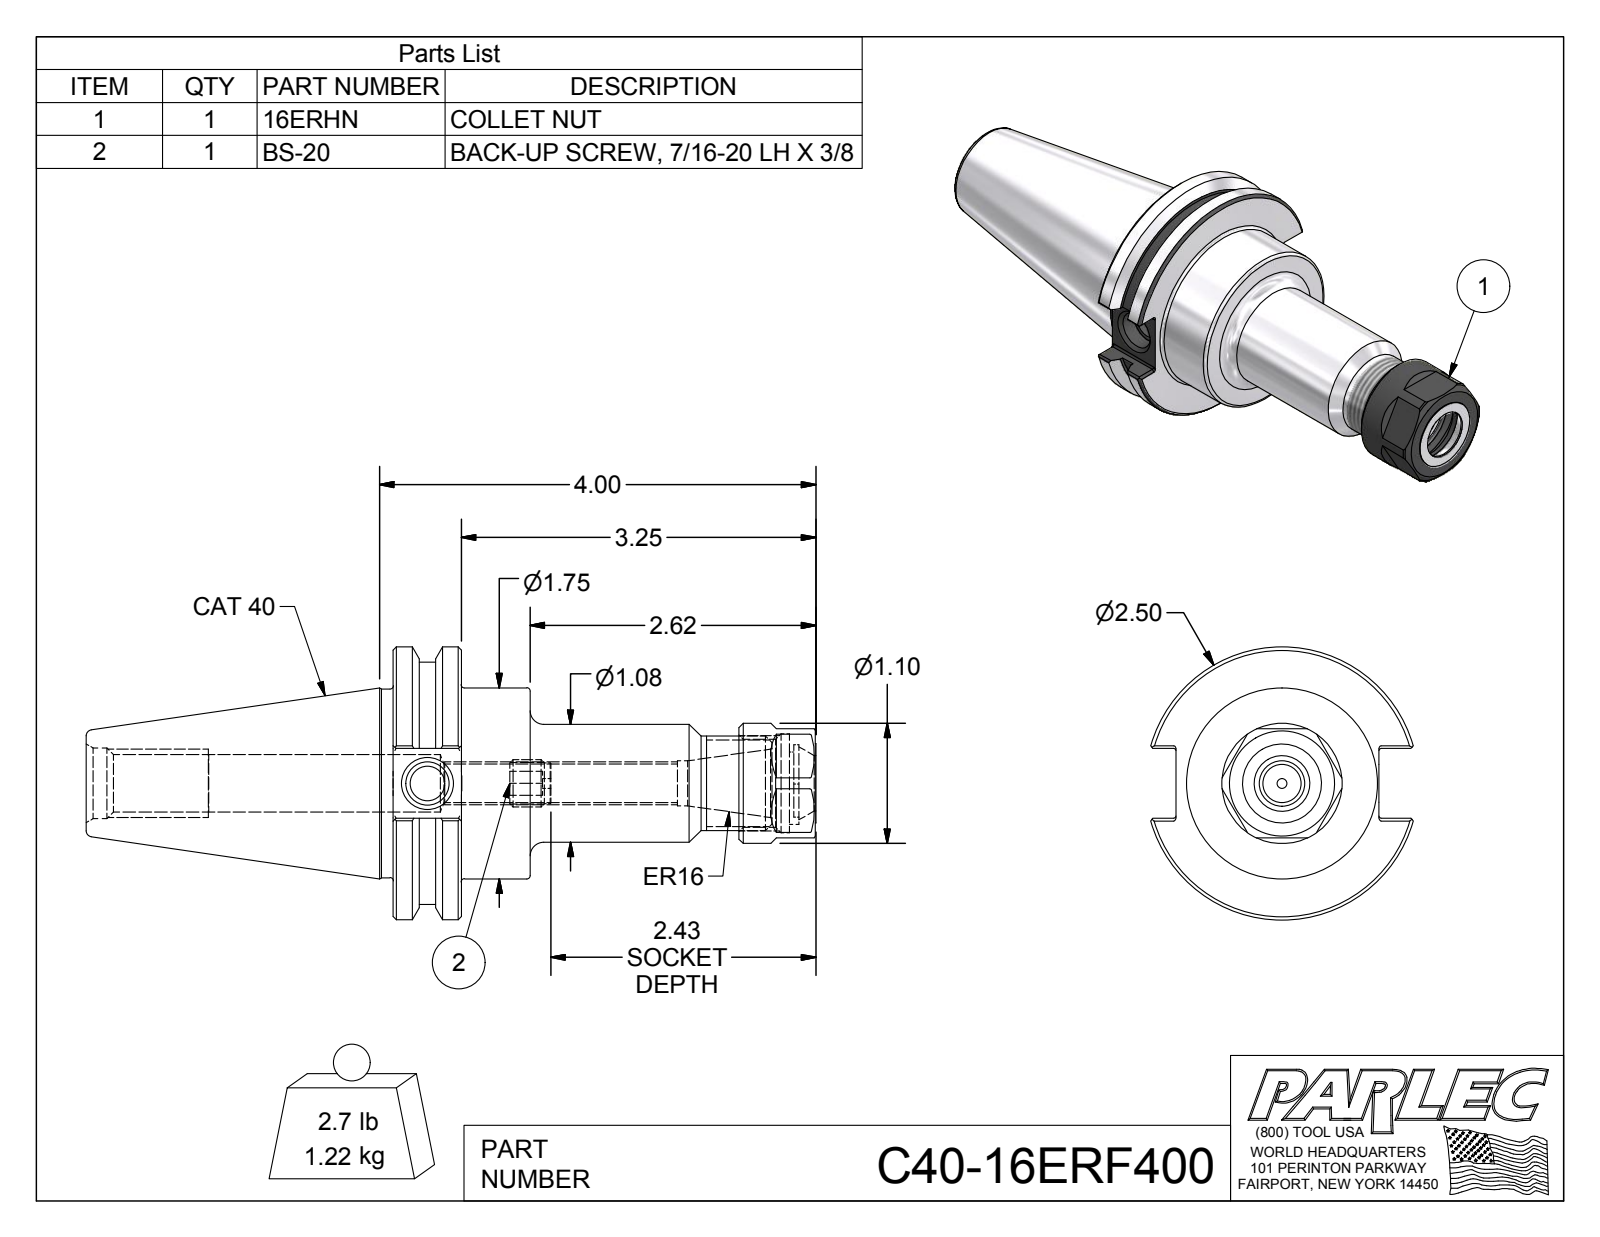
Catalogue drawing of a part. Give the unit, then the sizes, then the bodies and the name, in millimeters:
Units: millimetres
Overall size (bounding box): 169.86 × 63.5 × 61.05
Round holes (diameter × count): ⌀2.29 ×1, ⌀8 ×1, ⌀8.92 ×1, ⌀10.13 ×1, ⌀10.5 ×1, ⌀12.4 ×1, ⌀13.38 ×1, ⌀13.39 ×1, ⌀16.46 ×1, ⌀17.02 ×1, ⌀20.5 ×1, ⌀23 ×1
Round bosses / shafts (diameter × count): ⌀63.5 ×1, ⌀56.36 ×1, ⌀44.45 ×1, ⌀43.94 ×1, ⌀28 ×1, ⌀27.43 ×1, ⌀22 ×1, ⌀10.97 ×1
Partial cylindrical surfaces — rounded edges, fillets, slot ends (radius × count): R0.51 ×12, R7.24 ×1, R9 ×1
Main face-to-face distances: 15.88, 31.88, 16, 98.43, 82.55, 66.55, 25.14, 4.44, 20.7, 92.73
Hole centre spacings: 1.52
Volume: 154 451 mm³ · Surface area: 33 018 mm²
Bodies: 3 solids, 137 faces (59 planar, 39 cylindrical, 39 other)
Part name (STEP PRODUCT): C40-16ER4-1; 16ERHN; BS-20; C40-16ERF400
STEP written by: Autodesk Inventor 2016 (AUTOMOTIVE_DESIGN)
